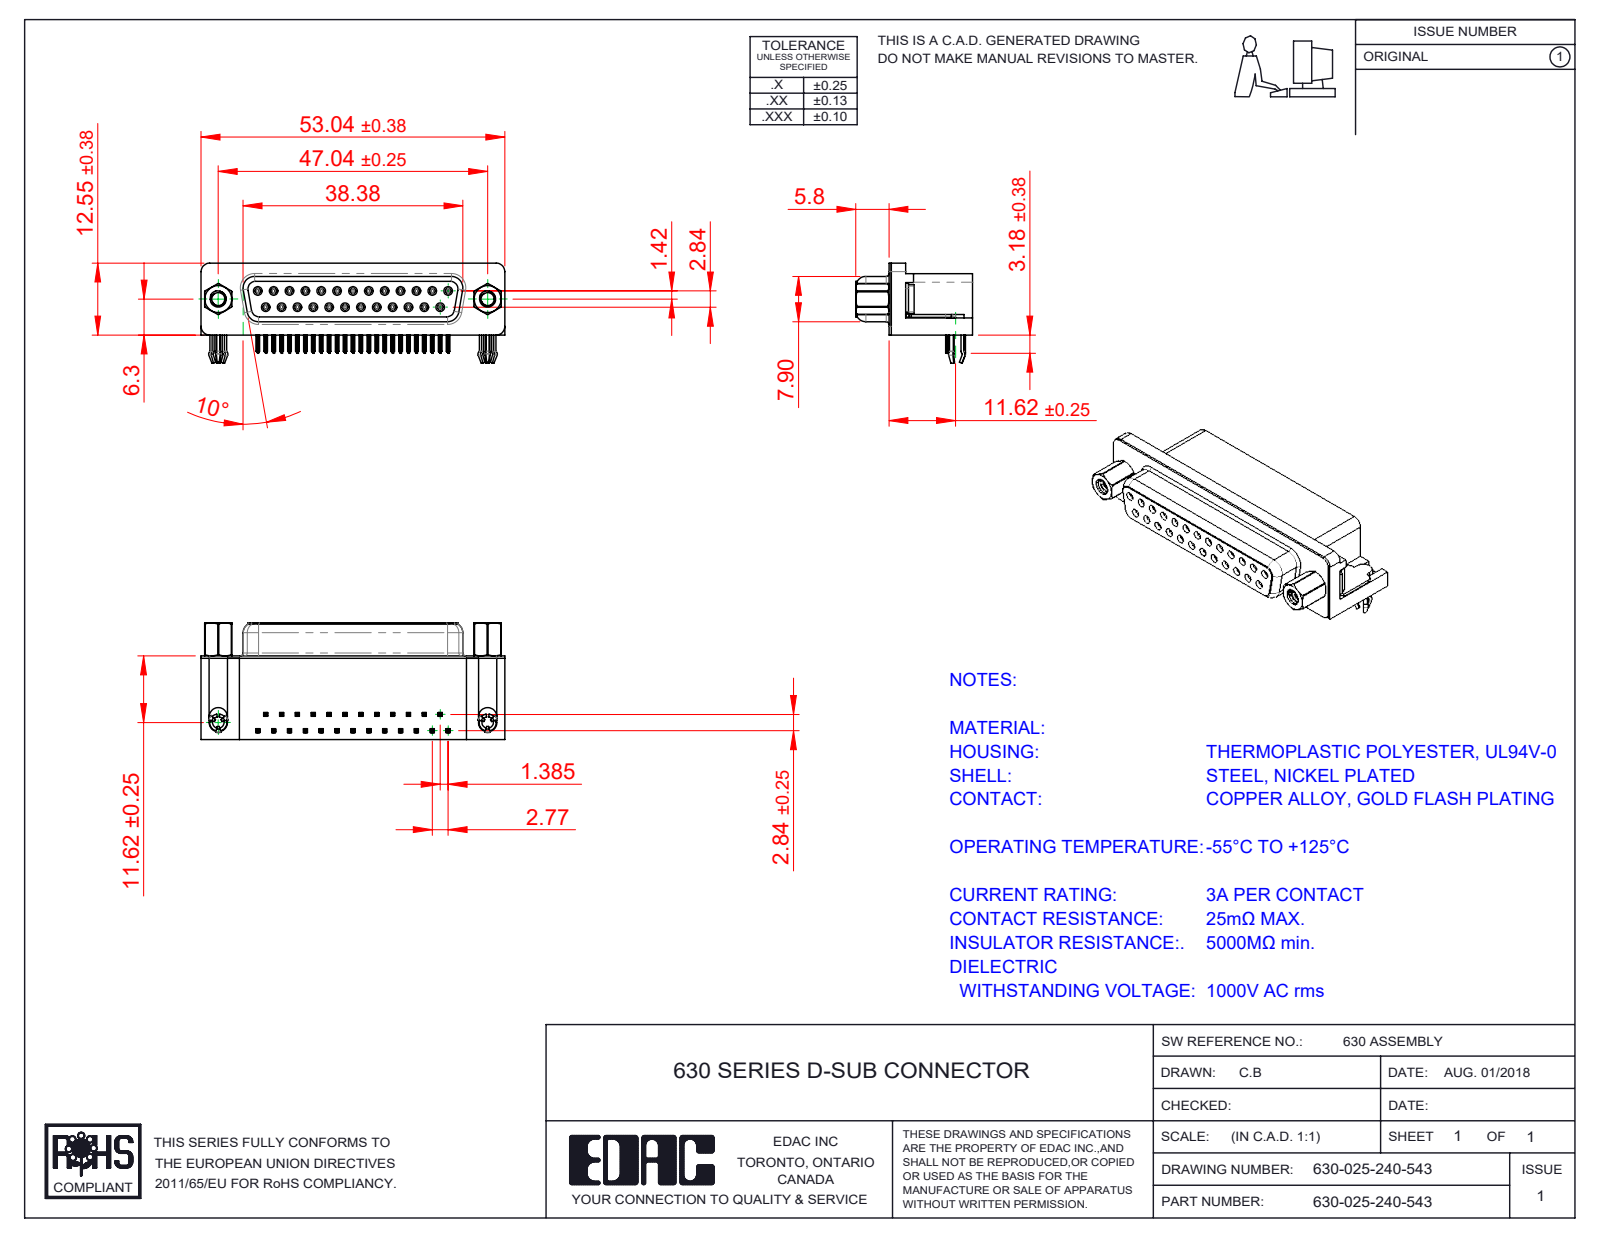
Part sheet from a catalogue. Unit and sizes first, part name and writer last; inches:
Units: inches
Overall size (bounding box): 2.088 × 0.803 × 0.688
Round holes (diameter × count): ⌀0.031 ×25, ⌀0.035 ×25, ⌀0.079 ×2, ⌀0.089 ×2, ⌀0.09 ×2, ⌀0.157 ×2, ⌀0.189 ×2, ⌀0.197 ×2
Round bosses / shafts (diameter × count): ⌀0.047 ×25, ⌀0.193 ×2, ⌀0.187 ×2, ⌀0.154 ×2, ⌀0.118 ×2, ⌀0.11 ×2
Partial cylindrical surfaces — rounded edges, fillets, slot ends (radius × count): R0.004 ×200, R0.006 ×100, R0.014 ×50, R0.013 ×25, R0.039 ×18, R0.01 ×12, R0.011 ×12, R0.053 ×8
Main face-to-face distances: 0.016, 0.244, 0.407, 0.559, 0.107, 0.575, 0.033, 0.262, 0.112, 0.228
Hole centre spacings: 0.124, 0.109, 0.218, 0.327, 0.436, 0.198, 0.198, 0.294
Volume: 0.538 in³ · Surface area: 16.51 in²
Bodies: 33 solids, 4080 faces (1782 planar, 998 cylindrical, 1300 other)
Part name (STEP PRODUCT): 630 Shell_25 Socket; 630 3 Prong Board Lock; 630 4-40 Threaded Rivet; 630 4-40 Hex Standoff 5 (+4 more)
STEP written by: SolidWorks 2020 (CONFIG_CONTROL_DESIGN)
